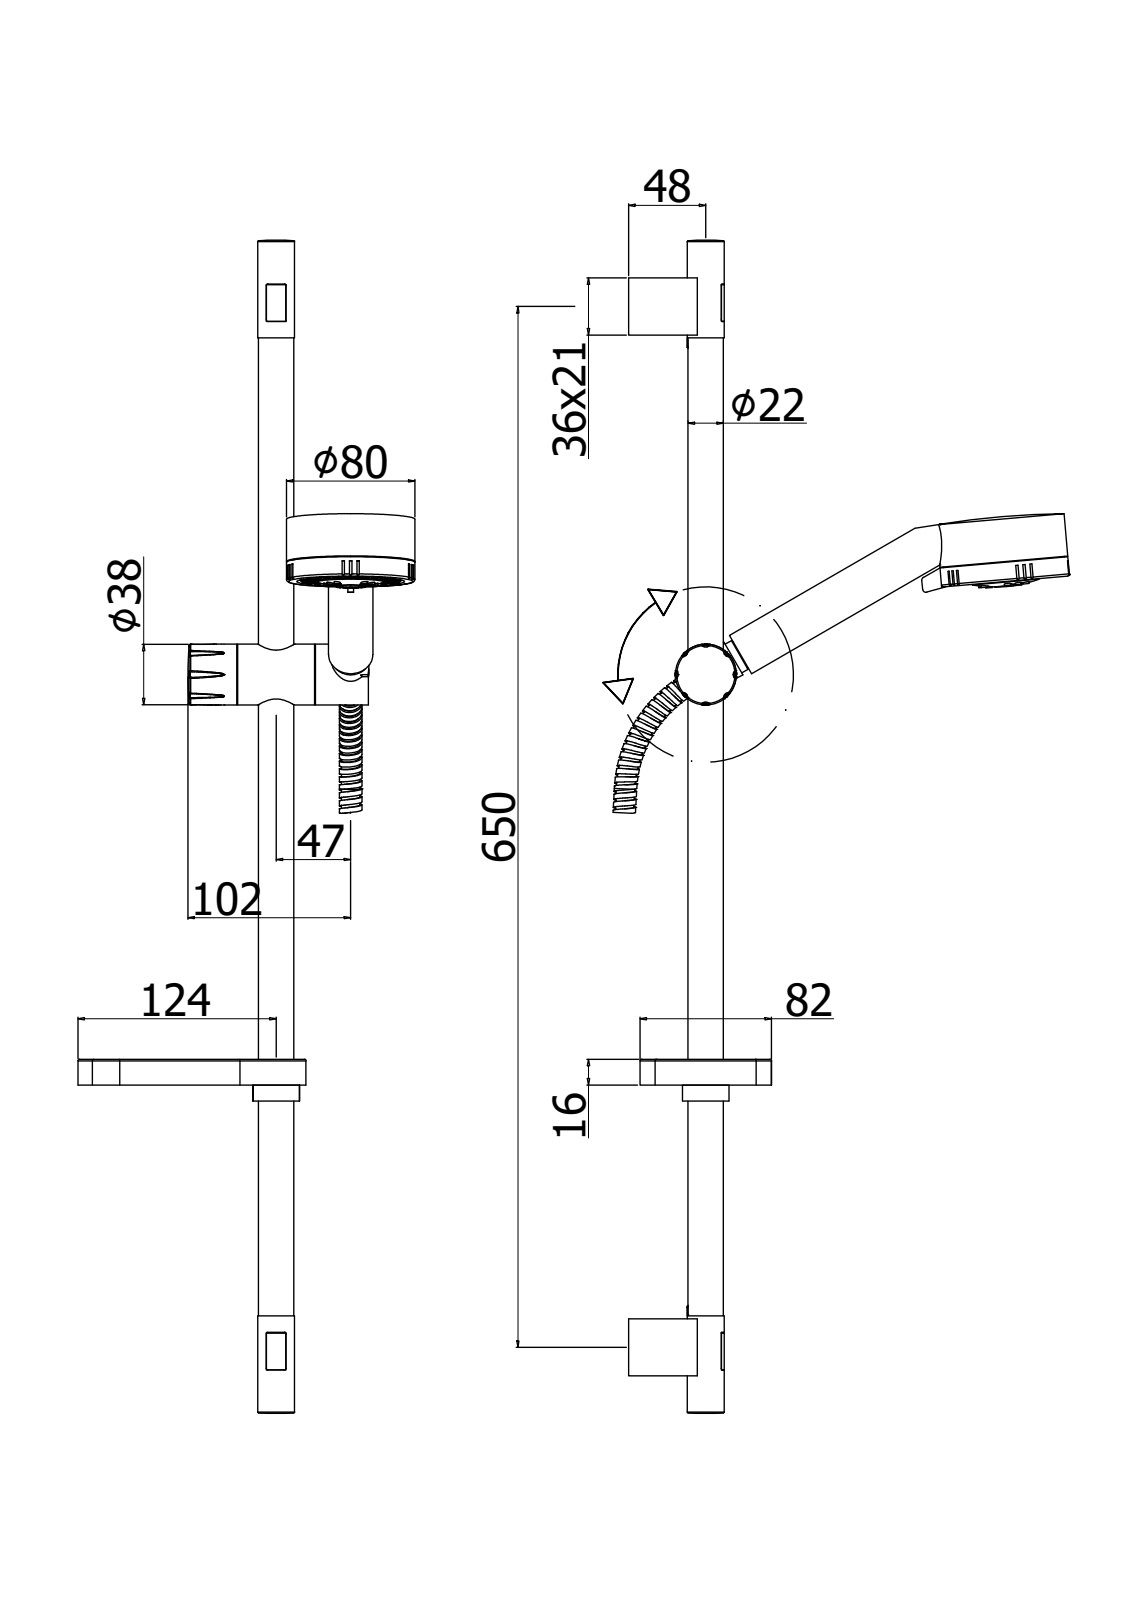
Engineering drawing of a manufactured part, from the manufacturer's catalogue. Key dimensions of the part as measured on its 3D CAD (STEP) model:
Part name (STEP PRODUCT): ZSAL110CR
STEP written by: CREO PARAMETRIC BY PTC INC, 2020044 (CONFIG_CONTROL_DESIGN)
Units: millimetres
Bodies: 7 solids, 2689 faces (636 planar, 690 cylindrical, 1363 other)
Overall size (bounding box): 706 × 217.87 × 211.68
Volume: 318 761 mm³ · Surface area: 296 069 mm²
Round holes (diameter × count): ⌀2.5 ×63, ⌀3 ×6, ⌀15.3 ×2, ⌀3.4 ×1, ⌀8.5 ×1, ⌀9.3 ×1, ⌀10 ×1, ⌀11 ×1, ⌀12 ×1, ⌀13.7 ×1, ⌀14 ×1, ⌀15.6 ×1
Round bosses / shafts (diameter × count): ⌀4 ×15, ⌀3 ×8, ⌀15 ×2, ⌀79.14 ×1, ⌀75.94 ×1, ⌀57 ×1, ⌀42.4 ×1, ⌀41.6 ×1
Partial cylindrical surfaces — rounded edges, fillets, slot ends (radius × count): R0.1 ×60, R1 ×60, R0.5 ×20, R1.24 ×15, R2.05 ×15, R0.78 ×4, R1.35 ×4, R1.42 ×4
Main face-to-face distances: 12.5, 2.5, 1.5, 2, 10, 4.4, 8.51, 4.11, 6.01, 1.61
Hole centre spacings: 15, 13.49, 13.5, 10.3, 15.01, 25.98, 10.31, 13.51
